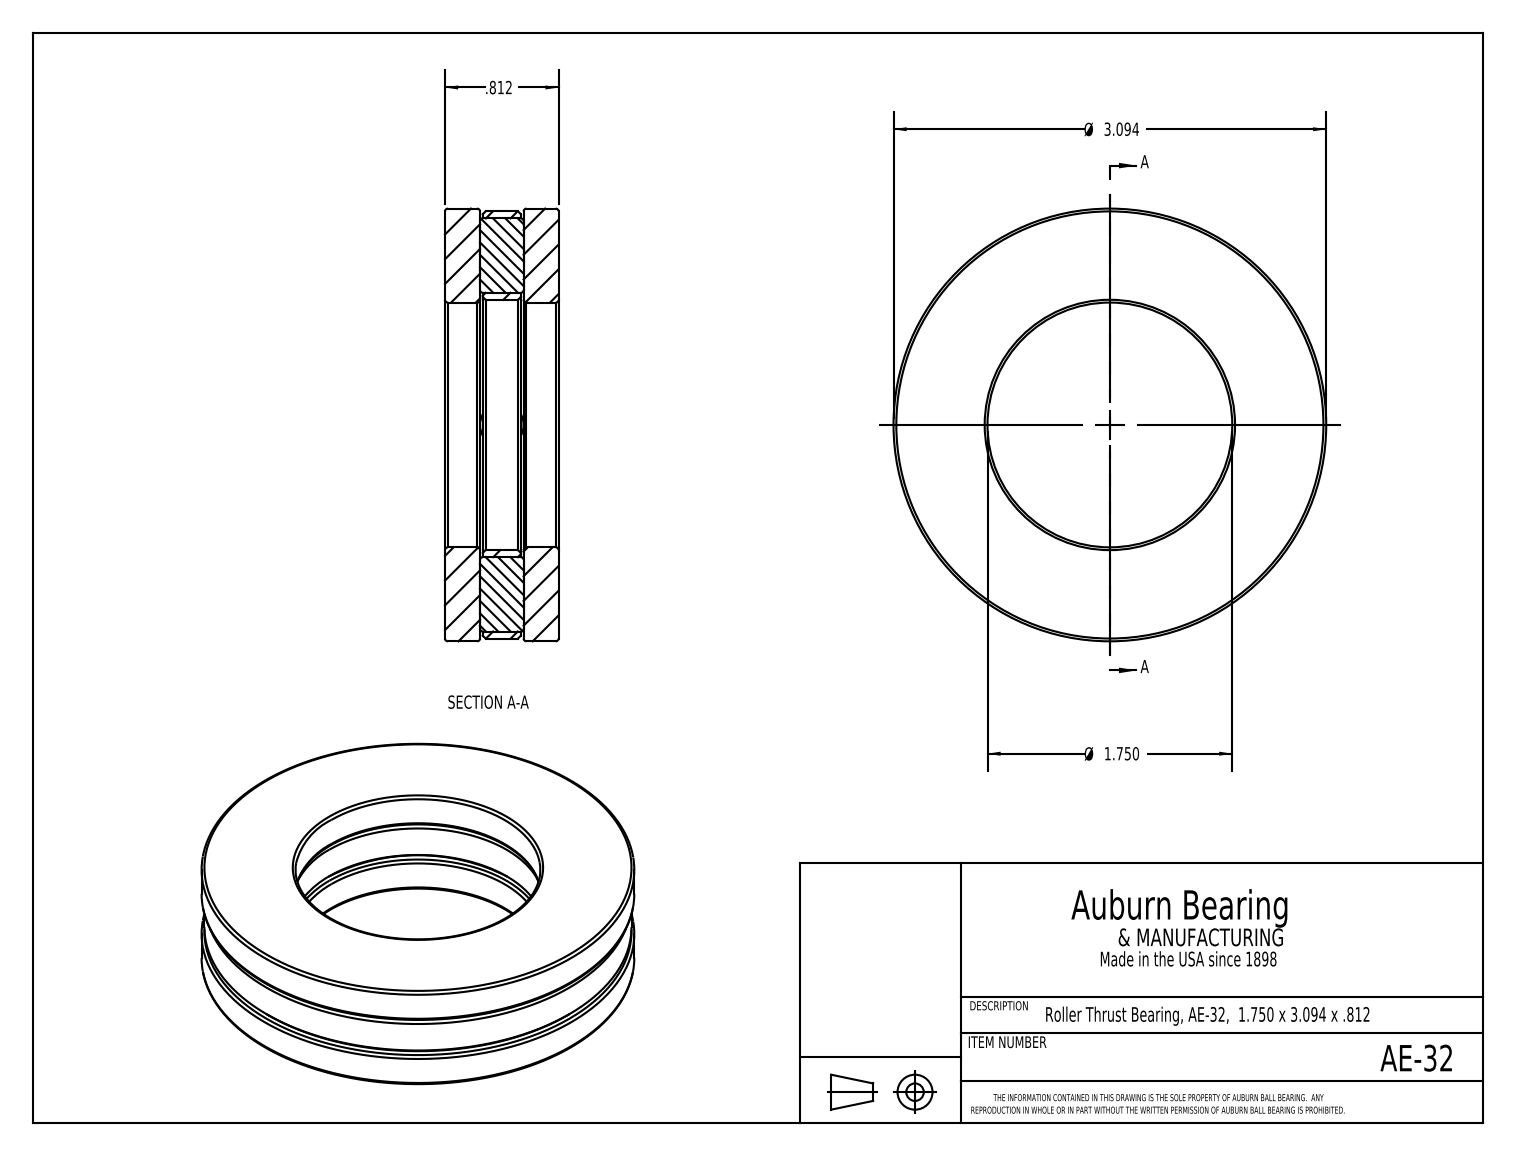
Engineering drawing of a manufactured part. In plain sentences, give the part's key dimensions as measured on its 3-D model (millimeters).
The part is named "AE-32". Its 3-D file was written by "SolidWorks 2017 (CONFIG_CONTROL_DESIGN)". It is 7 solids with 60 faces: 30 planar, 10 cylindrical and 20 other. Overall it measures 78.6 by 78.6 by 20.6 millimeters. Its volume is 62 830 cubic millimeters and its surface area 28 430 square millimeters. Round holes: 1 of diameter 44.5, 1 of diameter 45.5. Round bosses or shafts: 2 of diameter 7.9, 1 of diameter 78.6, 1 of diameter 77.6. The main face-to-face distances are 6.4, 14.3, 6.9, 13.8, 0.5, 7.4, 7.9, 20.6, 6.9, 20.
